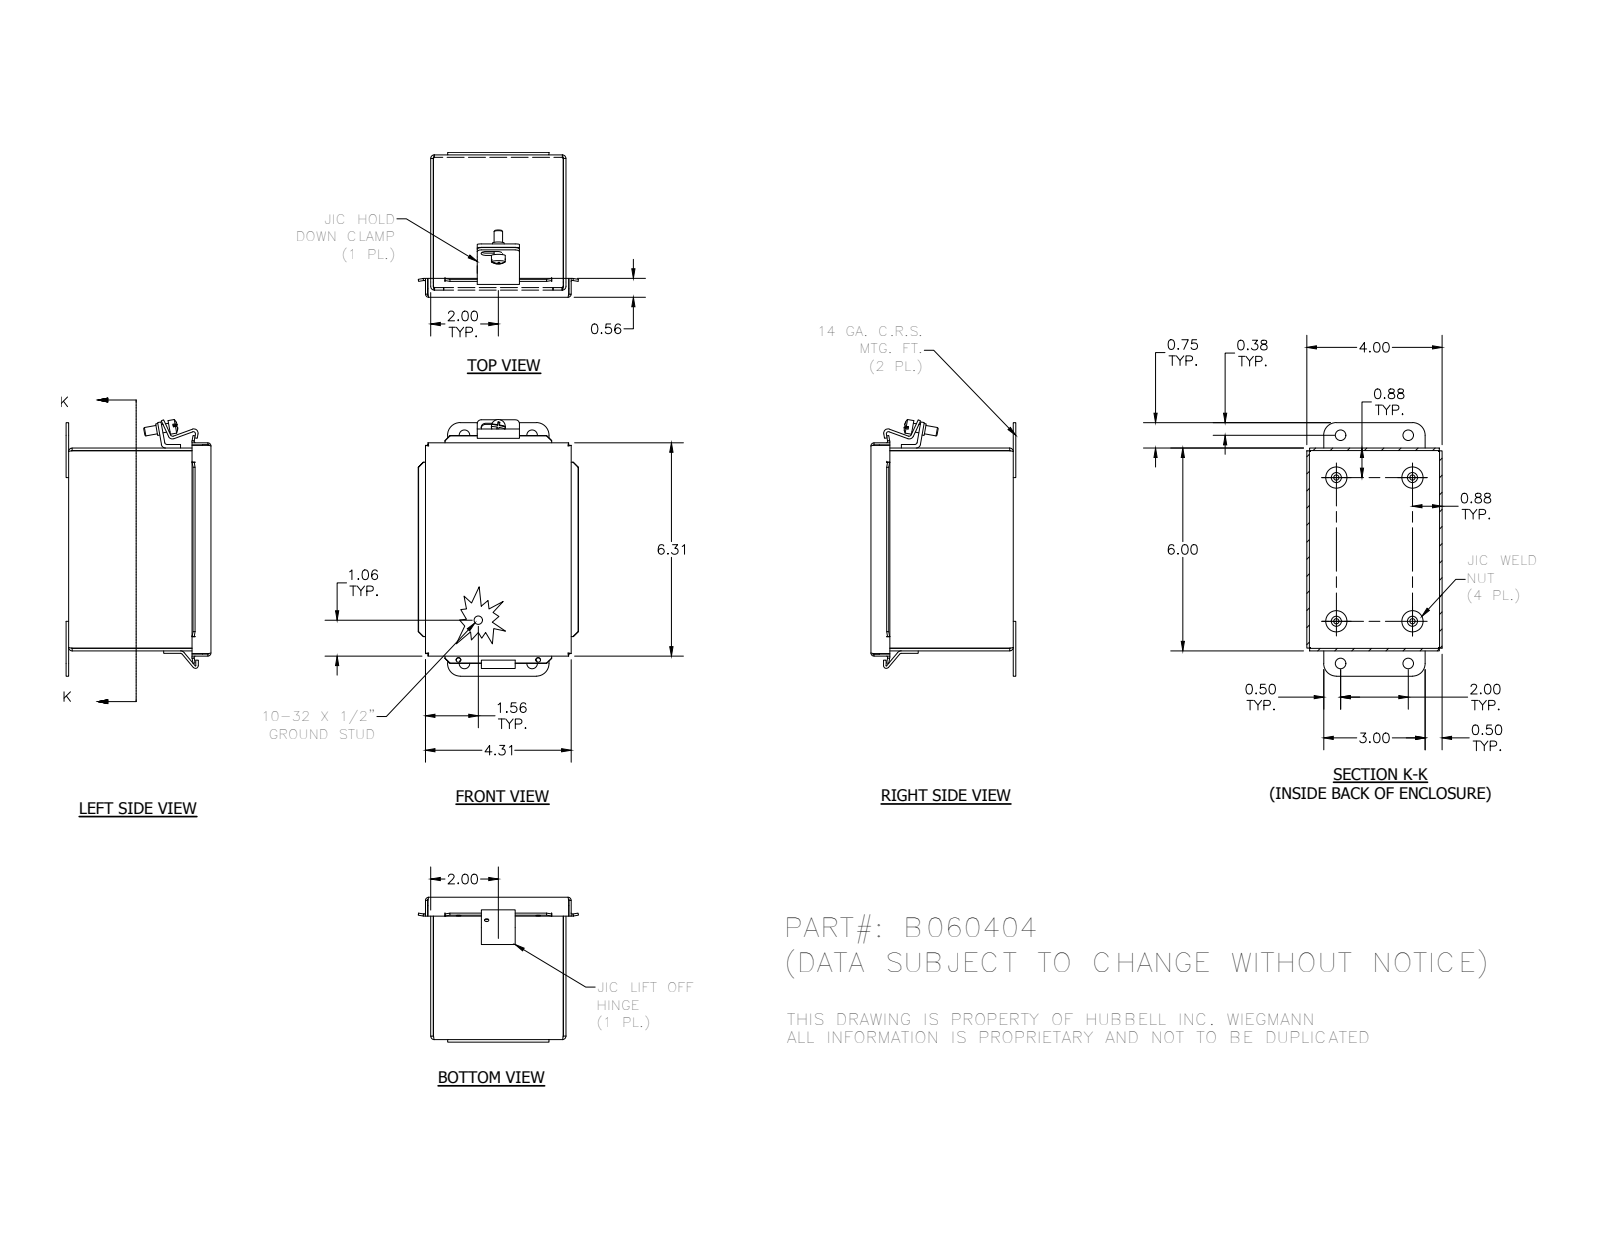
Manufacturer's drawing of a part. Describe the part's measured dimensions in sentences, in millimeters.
The part is named "B060404; 3499; 3481; C1001 (+7 more)". Its 3-D file was written by "Autodesk Inventor 2012 (AUTOMOTIVE_DESIGN)". It is 15 solids with 346 faces: 227 planar, 77 cylindrical and 42 other. Overall it measures 192.9 by 120.4 by 108.9 millimeters. Its volume is 224 800 cubic millimeters and its surface area 233 900 square millimeters. Round holes: 4 of diameter 4, 4 of diameter 7.9, 2 of diameter 3.6, 1 of diameter 3.2, 1 of diameter 5. Round bosses or shafts: 4 of diameter 15.9, 4 of diameter 7.6, 2 of diameter 6.4, 1 of diameter 10.4, 1 of diameter 8.7, 1 of diameter 4.8. Partial cylindrical surfaces (rounded edges, fillets, slot ends): 16 of radius 0.8, 8 of radius 2.4, 8 of radius 2.7, 4 of radius 3.2, 4 of radius 9.5, 3 of radius 1.6, 3 of radius 3.2, 2 of radius 3.4. The main face-to-face distances are 1.9, 99.7, 105.4, 150.5, 101.6, 97.8, 107, 1.6, 103.5, 105.1. The hole center spacings are 31.9, 31.9, 50.8, 57.2, 62.6, 62.6, 108, 122.1.
